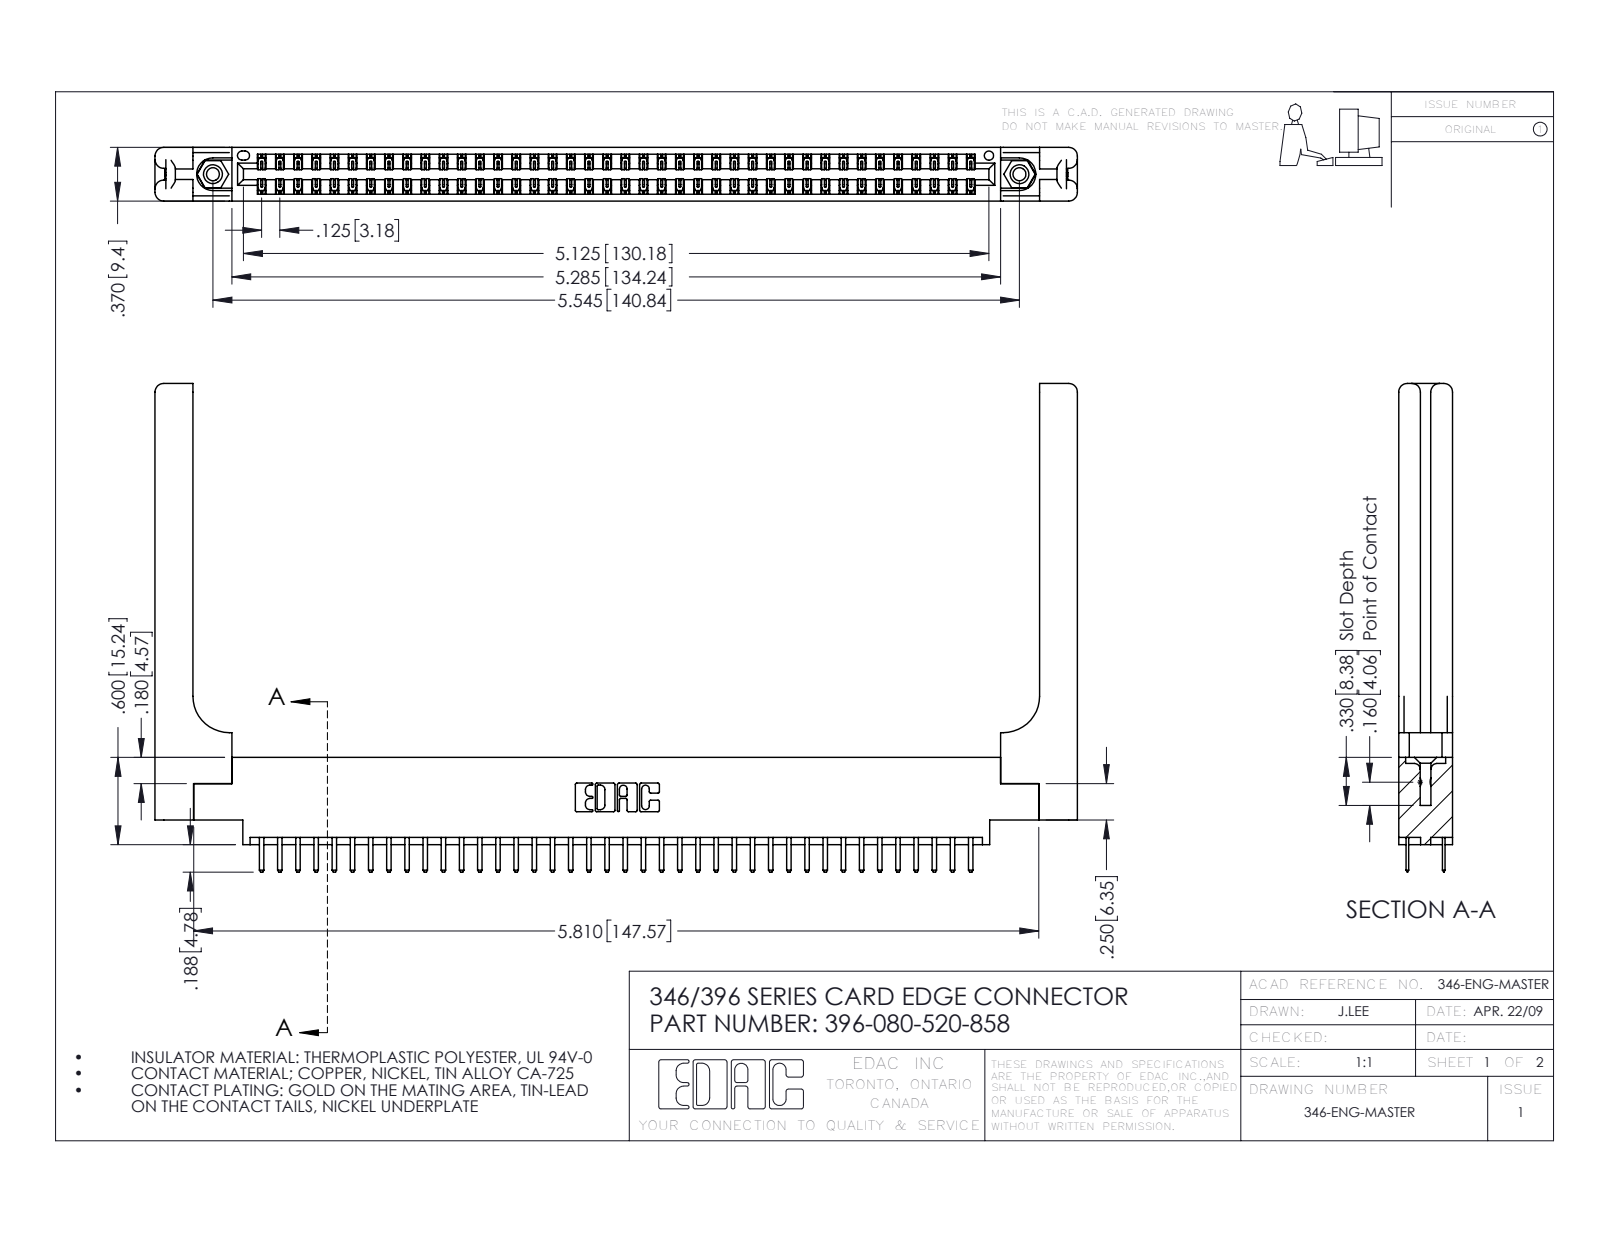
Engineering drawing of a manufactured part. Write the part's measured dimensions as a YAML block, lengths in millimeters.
part_name: "345-250-001_345-250-001-102; 345-292-001_345-293-120; 396-080-520-858; 346-220-058_345-220-058 (+1 more)"
step_written_by: "SolidWorks 2016 (CONFIG_CONTROL_DESIGN)"
units: millimeters
bodies: {solids: 85, faces: 4862, planar: 3188, cylindrical: 1614, other: 60}
overall_size: [161.1, 85.3, 9.4]
volume: 22990
surface_area: 26340
round_holes:
  - {diameter: 2.3, count: 2}
  - {diameter: 3.2, count: 2}
  - {diameter: 4, count: 2}
  - {diameter: 1.6, count: 1}
round_bosses_or_shafts:
  - {diameter: 3.9, count: 2}
partial_cylinders:
  - {radius: 0.2, count: 120}
  - {radius: 0.3, count: 84}
  - {radius: 0.3, count: 22}
  - {radius: 1.5, count: 16}
  - {radius: 0.2, count: 6}
  - {radius: 0.8, count: 6}
  - {radius: 0.7, count: 3}
  - {radius: 0.4, count: 2}
face_to_face_distances: [9.4, 1.2, 8.2, 1.8, 6.4, 3.8, 3.8, 7.6, 0.6, 7]
hole_center_spacings: [6.2, 135.5, 140.8]
